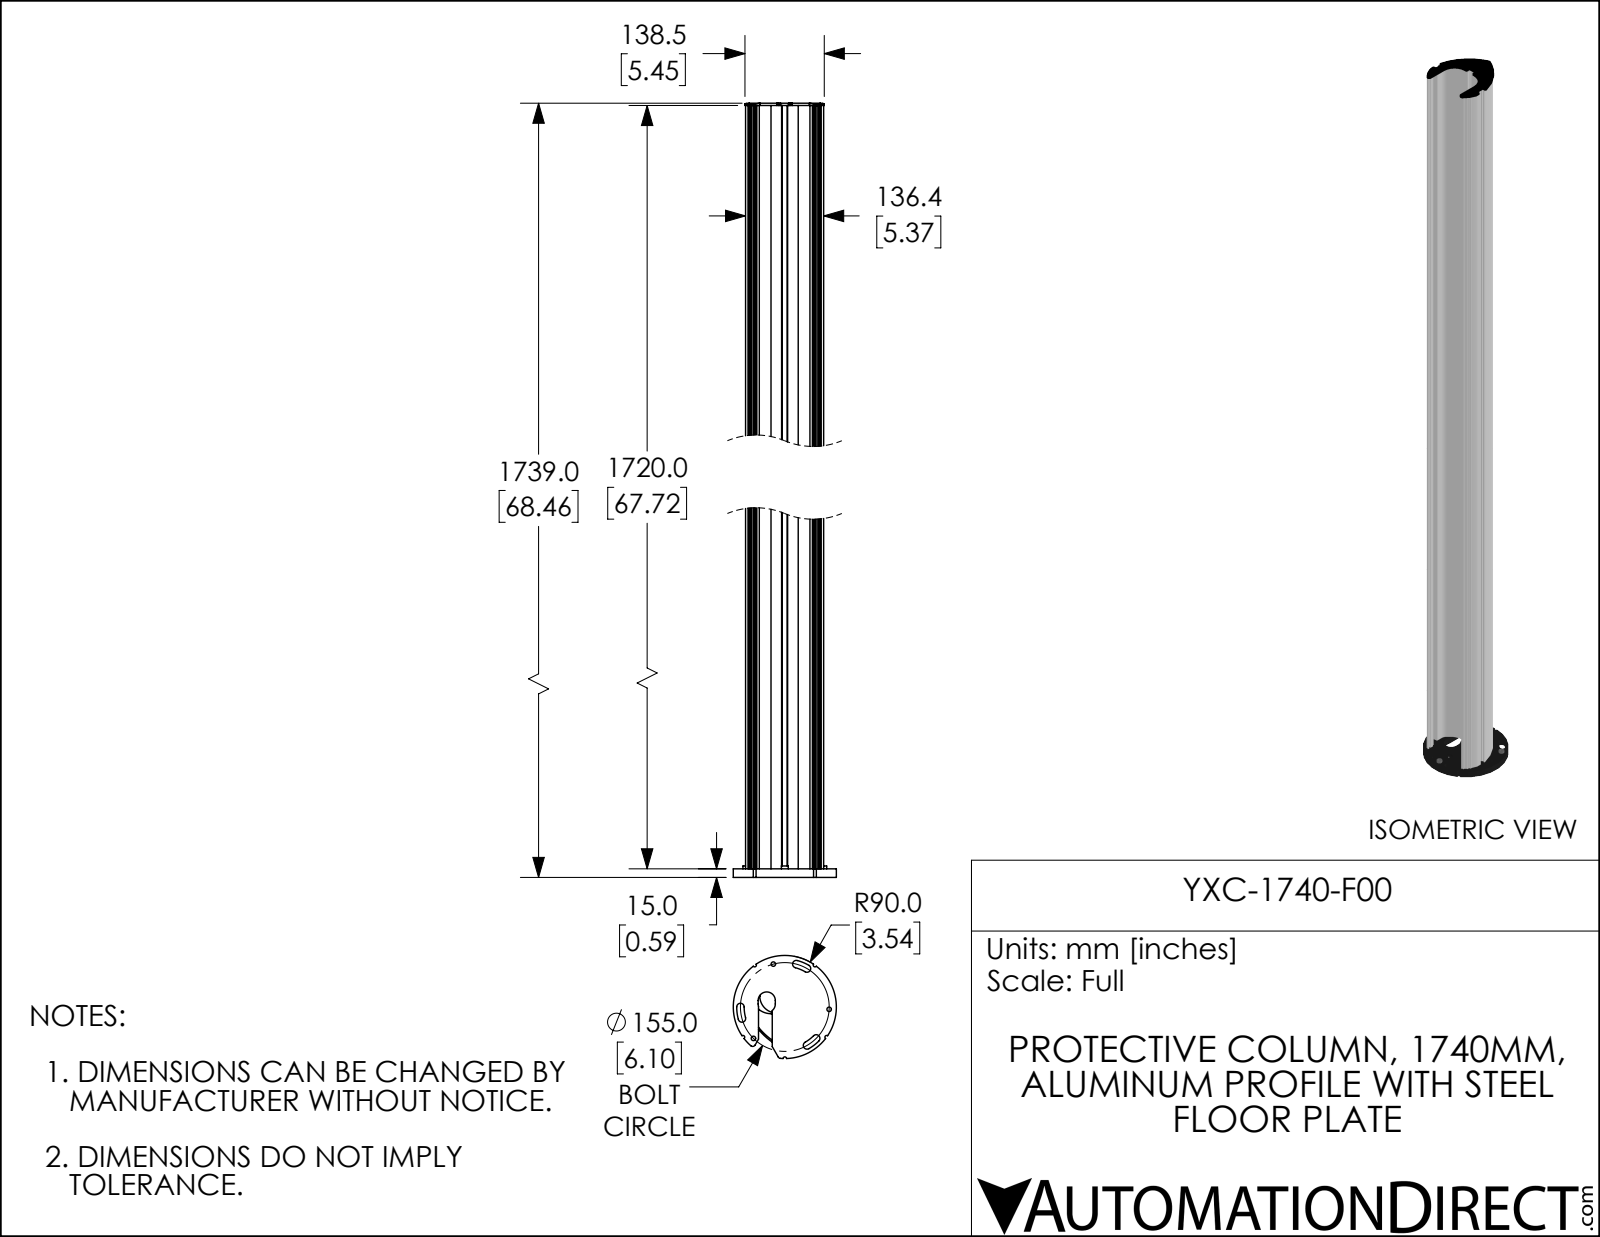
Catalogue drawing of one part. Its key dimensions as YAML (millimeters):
part_name: "YXC-1740-F00"
step_written_by: "SolidWorks 2019 (AUTOMOTIVE_DESIGN)"
units: millimeters
bodies: {solids: 1, faces: 326, planar: 201, cylindrical: 112, other: 13}
overall_size: [1739, 180, 180]
volume: 10050000
surface_area: 1345000
round_holes:
  - {diameter: 7.8, count: 3}
  - {diameter: 4.4, count: 1}
  - {diameter: 15, count: 1}
round_bosses_or_shafts:
  - {diameter: 12, count: 3}
  - {diameter: 7.4, count: 2}
  - {diameter: 180, count: 1}
partial_cylinders:
  - {radius: 3, count: 17}
  - {radius: 1, count: 6}
  - {radius: 1.3, count: 6}
  - {radius: 6.5, count: 6}
  - {radius: 15, count: 4}
  - {radius: 5, count: 3}
  - {radius: 6, count: 3}
  - {radius: 1.5, count: 2}
face_to_face_distances: [11.5, 3, 124.9, 19.7, 116.7, 8.2, 105.2, 8.5, 127.9, 11.2]
hole_center_spacings: [31.9, 31.9, 94.4, 94.5, 118.3, 118.3, 125.4, 134.2]
